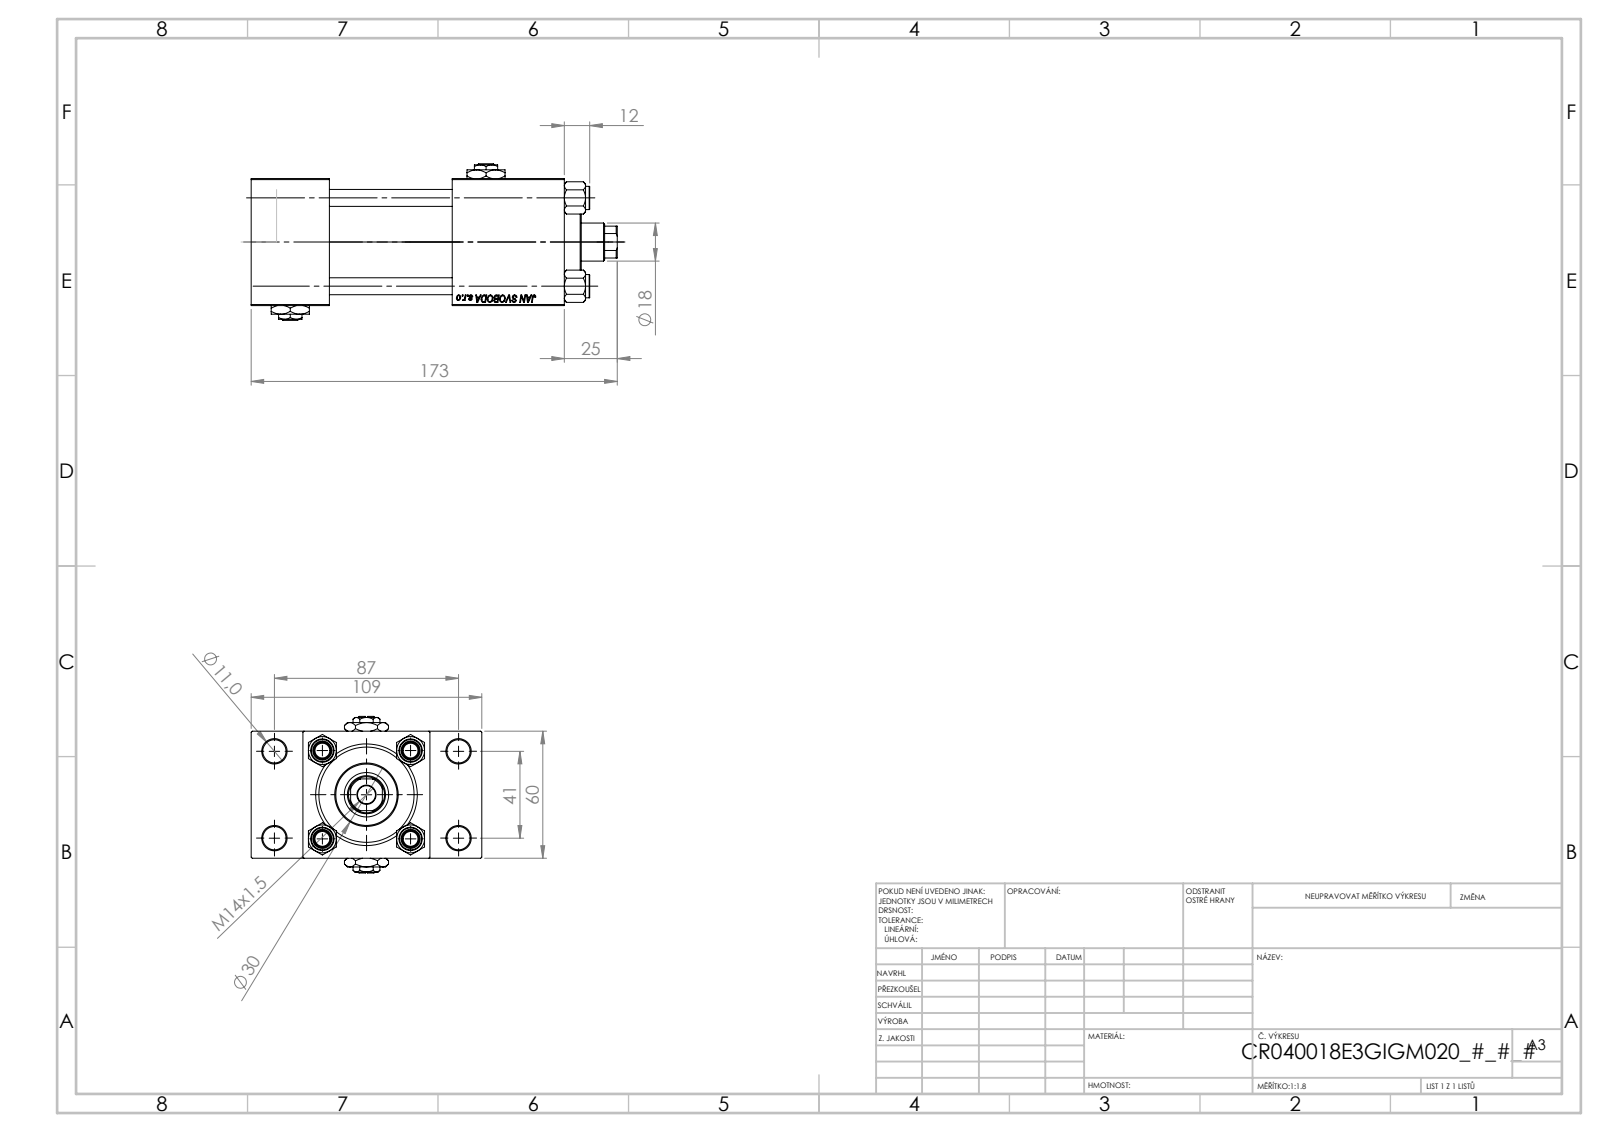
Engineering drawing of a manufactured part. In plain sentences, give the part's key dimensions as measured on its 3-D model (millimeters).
The part is named "V215CR_VCP_E; NUT_M5_E; Zatka_pro_OIL_PORT; V215CR_E_Body (+2 more)". Its 3-D file was written by "SolidWorks 2019 (CONFIG_CONTROL_DESIGN)". It is 13 solids with 1231 faces: 544 planar, 93 cylindrical and 594 other. Overall it measures 173 by 109 by 74 millimeters. Its volume is 499 540 cubic millimeters and its surface area 127 013 square millimeters. Round holes: 4 of diameter 8, 4 of diameter 11, 3 of diameter 7, 3 of diameter 16.66, 3 of diameter 24, 1 of diameter 8.5, 1 of diameter 18, 1 of diameter 21, 1 of diameter 31, 1 of diameter 40, 1 of diameter 45. Round bosses or shafts: 4 of diameter 11, 1 of diameter 46, 1 of diameter 30. Partial cylindrical surfaces (rounded edges, fillets, slot ends): 1 of radius 8.5. The main face-to-face distances are 60, 37, 24.5, 84.5, 148, 111, 24.3, 58, 53, 82.3. The hole center spacings are 22.65, 29.49, 41.7, 47.15, 48.09, 64.35, 76.49, 41.
